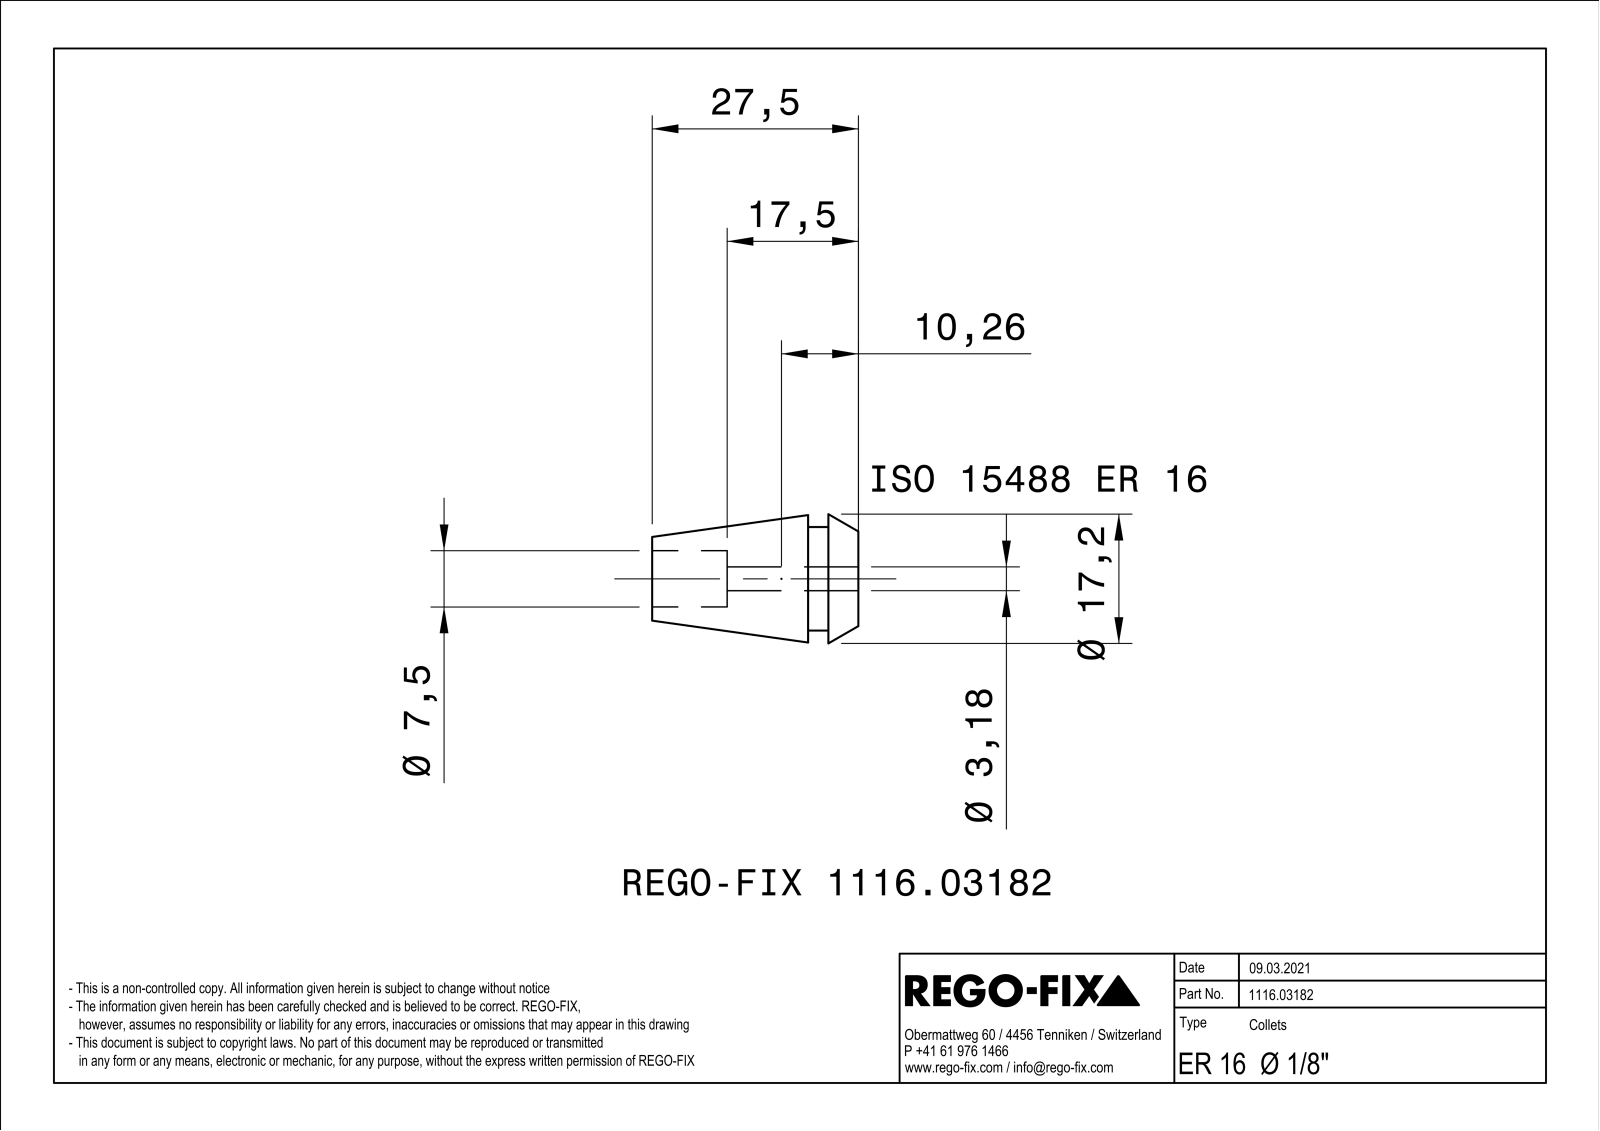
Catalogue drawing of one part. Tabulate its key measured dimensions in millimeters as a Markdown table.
| quantity | value |
| --- | --- |
| part name | NOCUT |
| STEP written by | SIEMENS PLM Software Solid Edge ST10 (AUTOMOTIVE_DESIGN) |
| units | millimeters |
| bodies | 1 solid, 240 faces (112 planar, 32 cylindrical, 96 other) |
| overall size | 27.5 × 17.24 × 17.24 |
| volume | 2 790 mm³ |
| surface area | 5 048 mm² |
| round holes (diameter × count) | 7.5 × 1 |
| partial cylindrical surfaces (radius × count) | 1.59 × 1, 6.9 × 1 |
| main face-to-face distances | 0.6, 3.2, 3.8, 4, 6.7, 2.7, 7, 27.5, 23.5, 20.8 |
